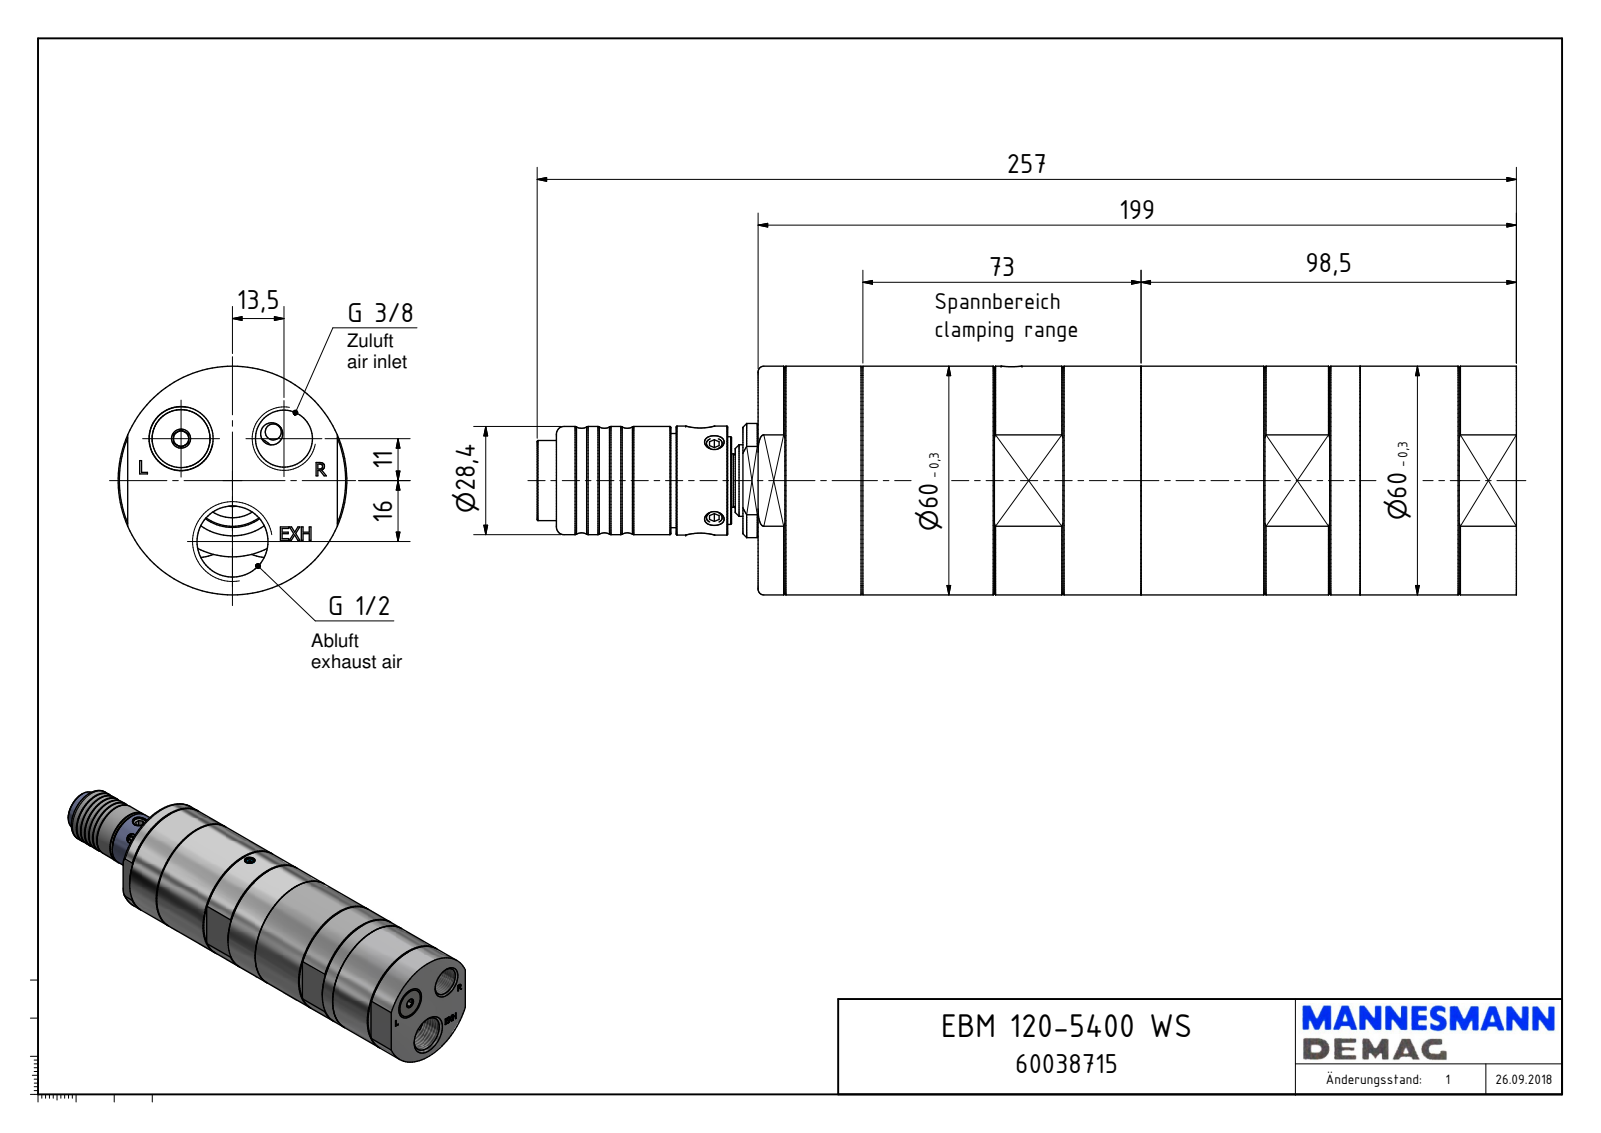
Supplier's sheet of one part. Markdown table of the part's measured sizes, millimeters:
| quantity | value |
| --- | --- |
| part name | EBM 120-5400 WS_60038715 |
| STEP written by | Autodesk Inventor 2014 (AUTOMOTIVE_DESIGN) |
| units | millimeters |
| bodies | 1 solid, 325 faces (156 planar, 91 cylindrical, 78 other) |
| overall size | 257 × 60 × 60 |
| volume | 580 057 mm³ |
| surface area | 57 809 mm² |
| round holes (diameter × count) | 3.5 × 2, 4.13 × 2, 1.55 × 1, 4 × 1, 5.5 × 1, 5.6 × 1, 6.65 × 1, 14.95 × 1, 18.63 × 1, 18.92 × 1, 24.9 × 1, 27.3 × 1 |
| round bosses / shafts (diameter × count) | 60 × 1, 55.18 × 1, 53.43 × 1, 29.95 × 1, 28.6 × 1, 28.4 × 1, 26.96 × 1, 24.8 × 1 |
| partial cylindrical surfaces (radius × count) | 2.5 × 2, 6.38 × 1, 8.33 × 1 |
| main face-to-face distances | 199, 55, 4, 16.5, 15, 187.85, 11.15, 27.5, 160.35, 171.5 |
| hole center spacings | 16, 32, 81.7 |
